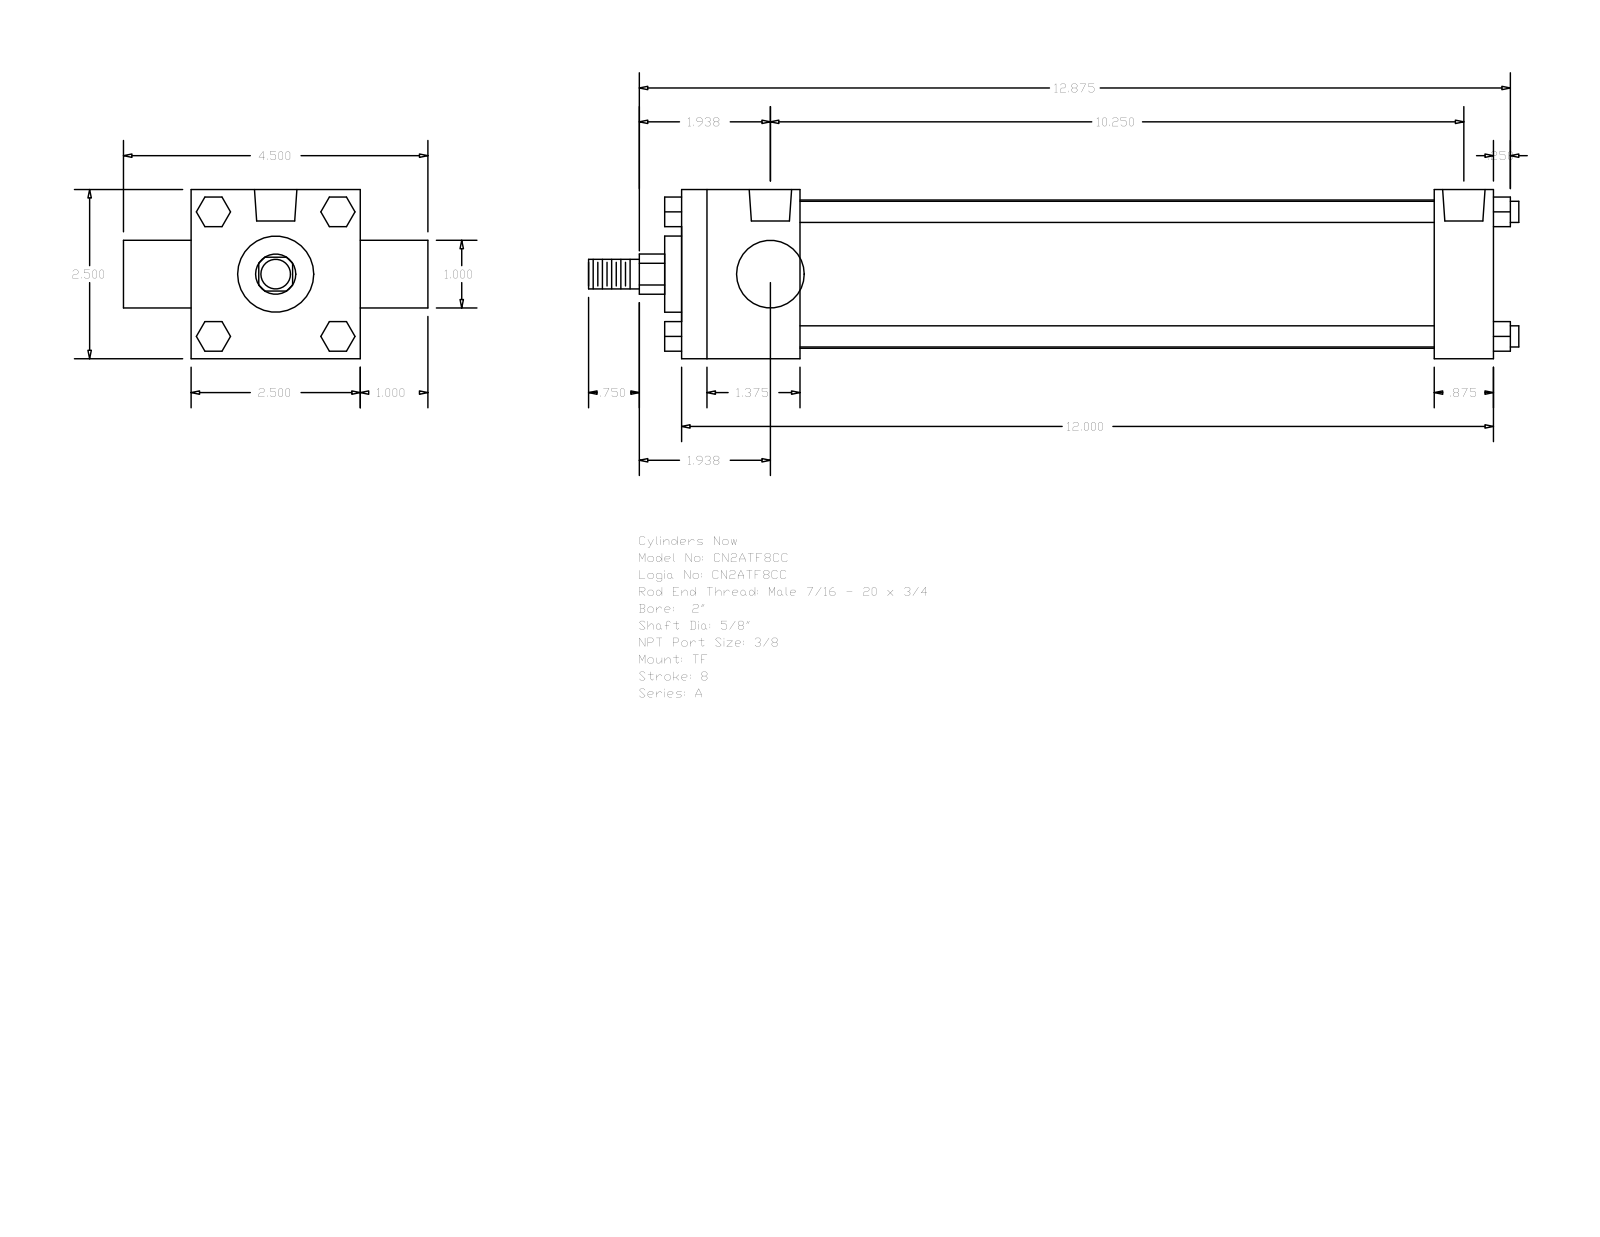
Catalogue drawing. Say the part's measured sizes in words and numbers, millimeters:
The part is named "A_TF__0200_0.625". Its 3-D file was written by "GSSL Pune (CONFIG_CONTROL_DESIGN)". It is 0 solids with 120 faces: 92 planar, 28 cylindrical and 0 other. Overall it measures 349.25 by 114.3 by 63.5 millimeters. Round holes: 3 of diameter 5.56, 2 of diameter 15.93. Round bosses or shafts: 4 of diameter 7.94, 1 of diameter 55.63, 1 of diameter 28.57, 1 of diameter 25.4, 1 of diameter 15.88, 1 of diameter 11.11. Partial cylindrical surfaces (rounded edges, fillets, slot ends): 1 of radius 7.54. The main face-to-face distances are 63.5, 304.8, 44.45, 282.57, 238.12, 260.35, 22.23, 25.4, 88.9, 50.8. The hole center spacings are 3.97, 3.98, 252.4, 256.37, 256.38, 260.35.
